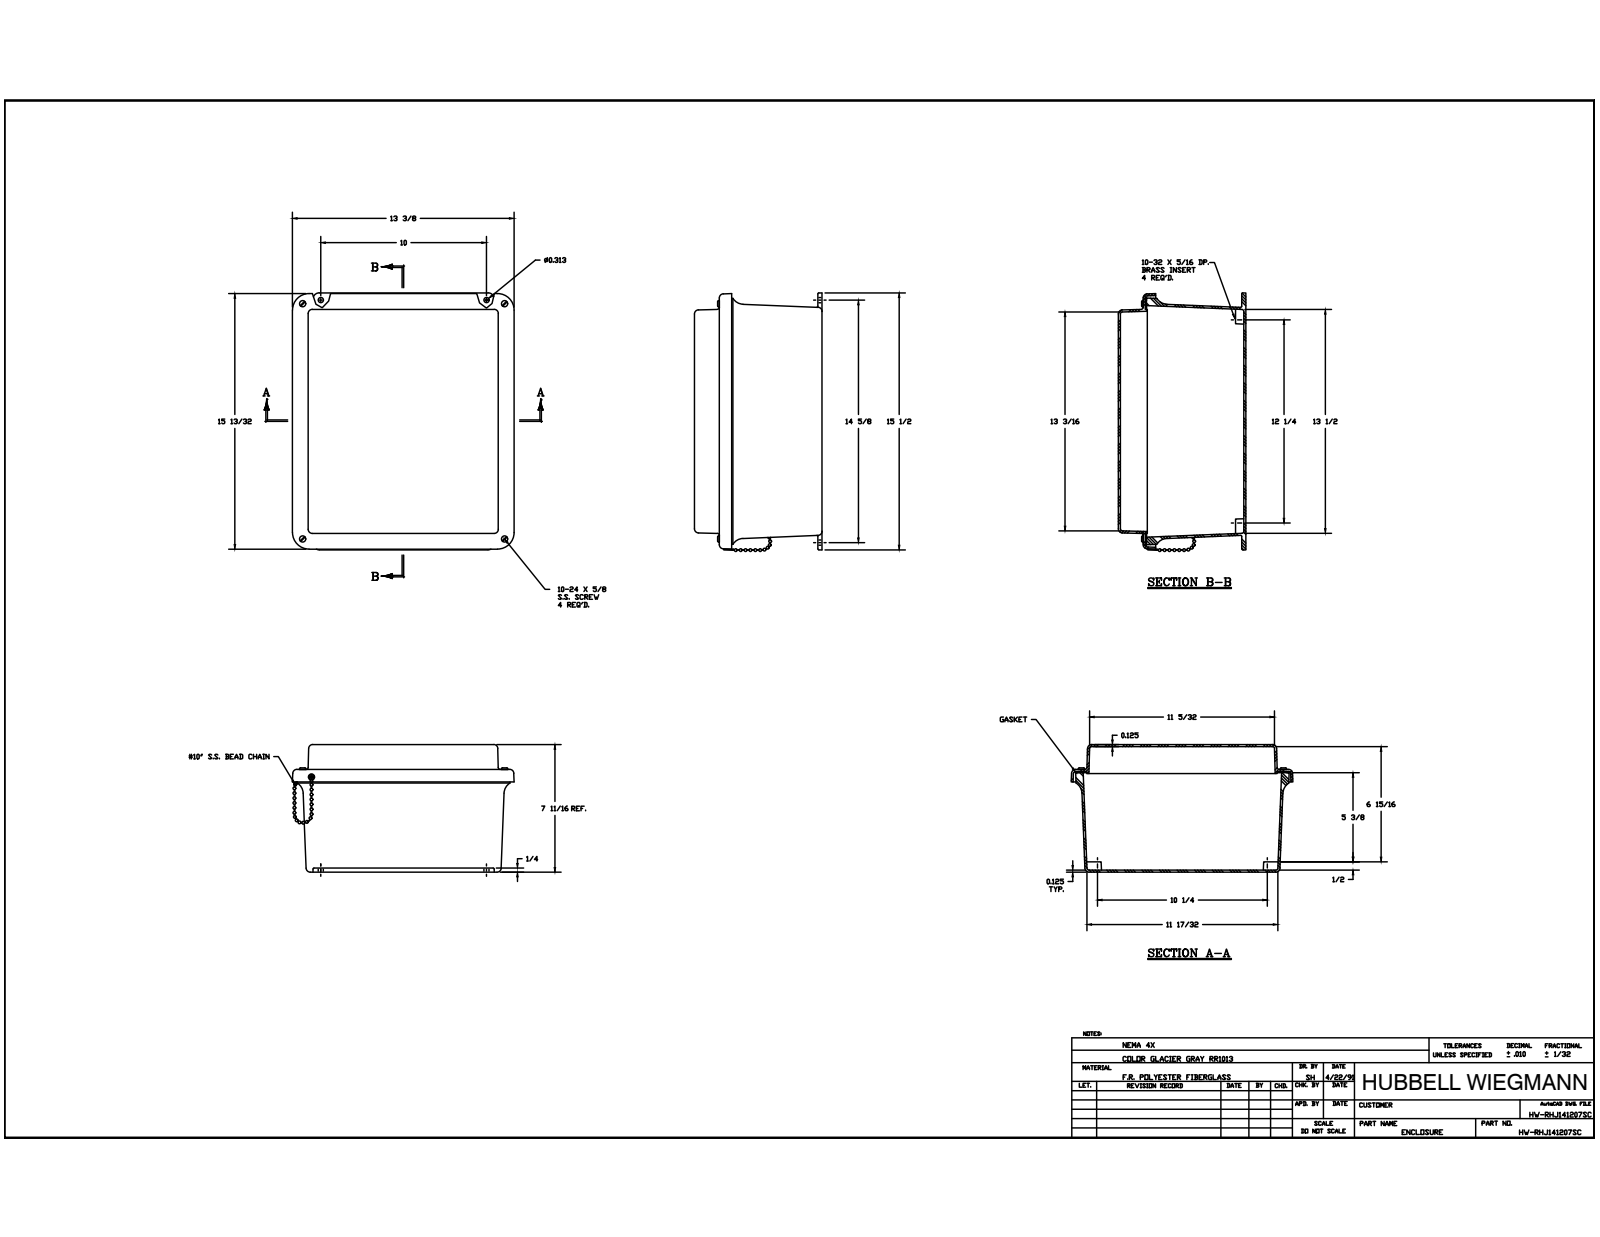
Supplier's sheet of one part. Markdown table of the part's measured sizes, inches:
| quantity | value |
| --- | --- |
| part name | J1412W_3; RMINS45821P_259; RMINS45821P_260; RMINS45821P_261 (+8 more) |
| STEP written by | Autodesk Inventor 2014 (AUTOMOTIVE_DESIGN) |
| units | inches |
| bodies | 21 solids, 925 faces (214 planar, 307 cylindrical, 404 other) |
| overall size | 16.087 × 13.712 × 7.689 |
| volume | 118.3 in³ |
| surface area | 1 676 in² |
| round holes (diameter × count) | 0.152 × 8, 0.14 × 6, 0.145 × 4, 0.156 × 4, 0.218 × 4, 0.187 × 2, 0.126 × 1 |
| round bosses / shafts (diameter × count) | 0.27 × 8, 0.19 × 4, 0.156 × 4, 0.375 × 2, 0.25 × 2, 0.125 × 2, 0.283 × 1 |
| partial cylindrical surfaces (radius × count) | 0.031 × 20, 0.125 × 20, 0.25 × 20, 0.2 × 4, 0.283 × 4, 0.375 × 4, 0.75 × 4, 0.01 × 2 |
| main face-to-face distances | 0.125, 0.125, 7.439, 7.564, 7.689, 7.564, 1.5, 5.939, 6.064, 1.625 |
| hole center spacings | 1.37, 11.26, 13.254, 17.337, 3.25, 6.5, 10.25, 12.187 |
